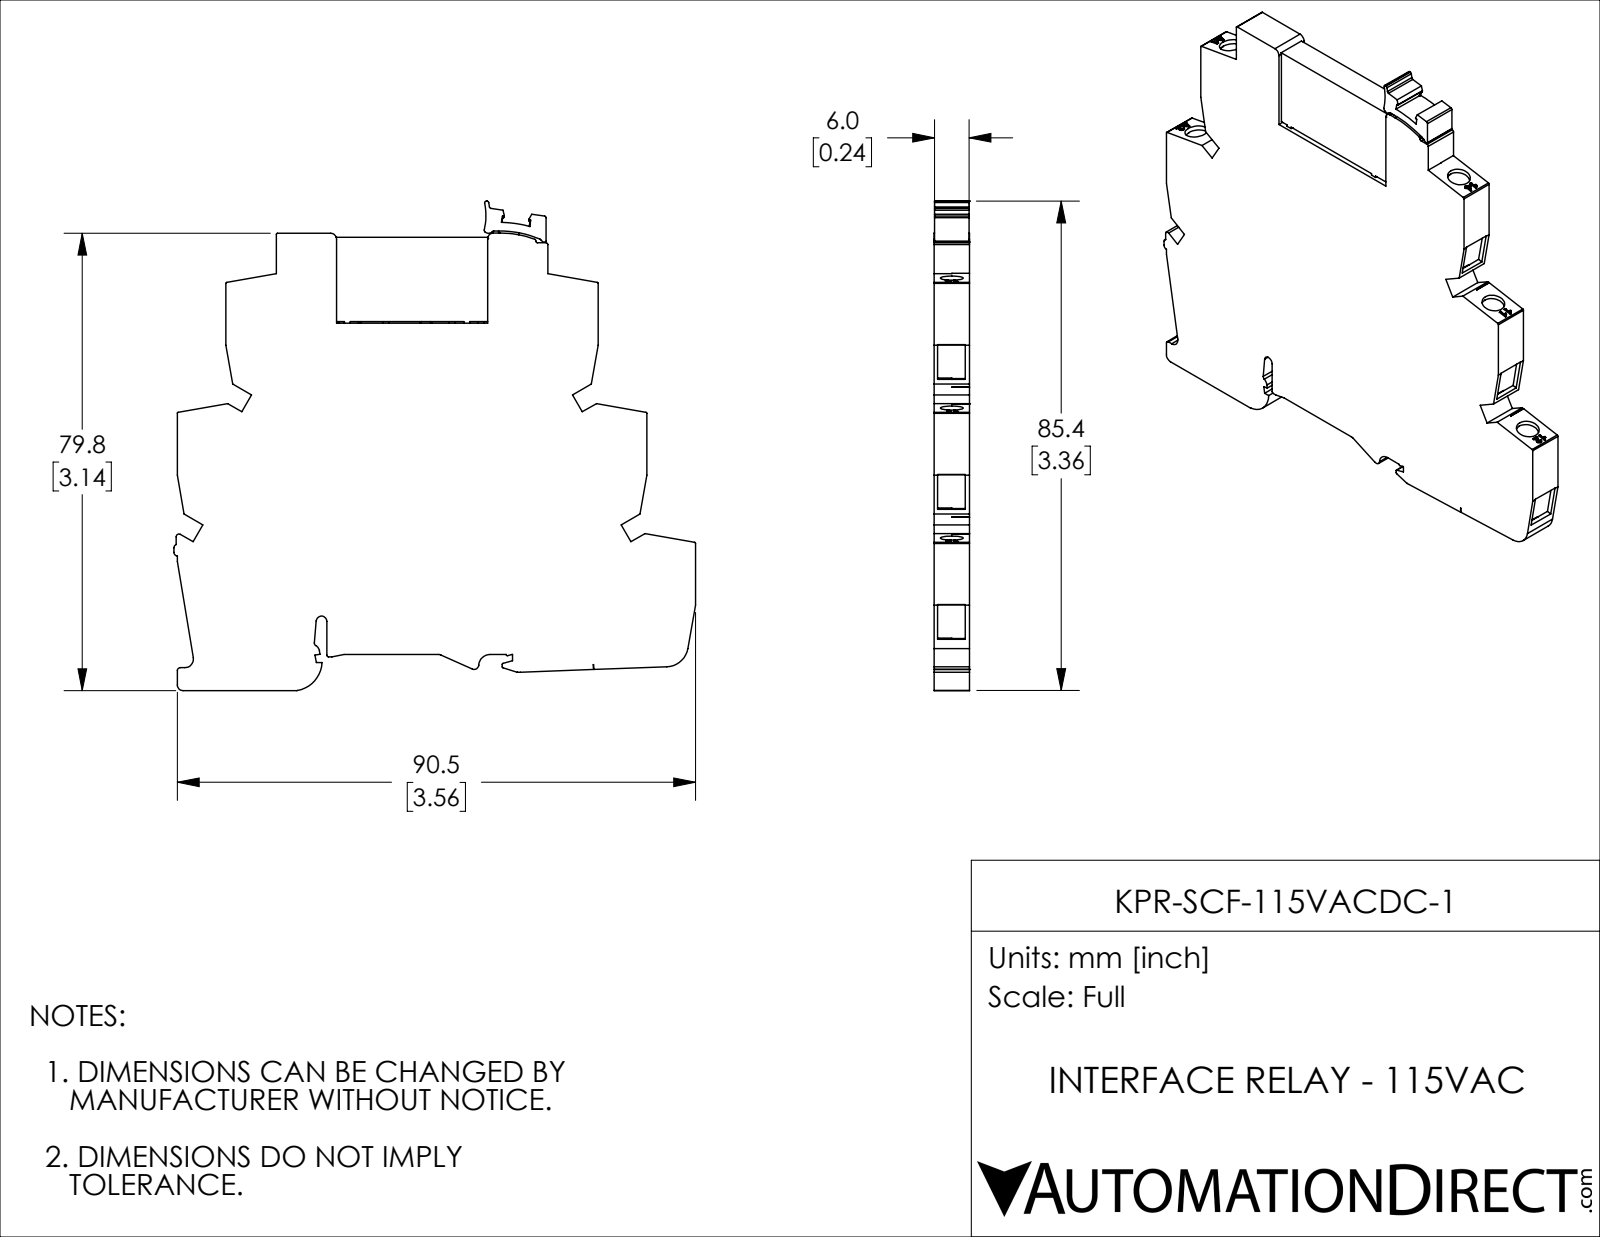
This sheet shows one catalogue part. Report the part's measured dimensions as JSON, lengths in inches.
{"part_name": "KPR-SCF-115VACDC-1", "step_written_by": "SolidWorks 2018 (AUTOMOTIVE_DESIGN)", "units": "inches", "bodies": {"solids": 1, "faces": 422, "planar": 304, "cylindrical": 90, "other": 28}, "overall_size": [3.586, 3.364, 0.244], "volume_in3": 2.104, "surface_area_in2": 23.55, "round_holes": [[0.157, 5]], "round_bosses_or_shafts": [[0.016, 2]], "partial_cylinders_radius": [[0.008, 15], [0.012, 10], [0.039, 10], [0.02, 5], [0.037, 5], [0.079, 3], [0.004, 2], [0.024, 2]], "face_to_face_distances": [0.244, 0.024, 0.22, 0.033, 0.197, 0.335, 0.031, 0.821, 3.228, 2.894], "hole_center_spacings": [0.485, 0.485, 0.969]}
